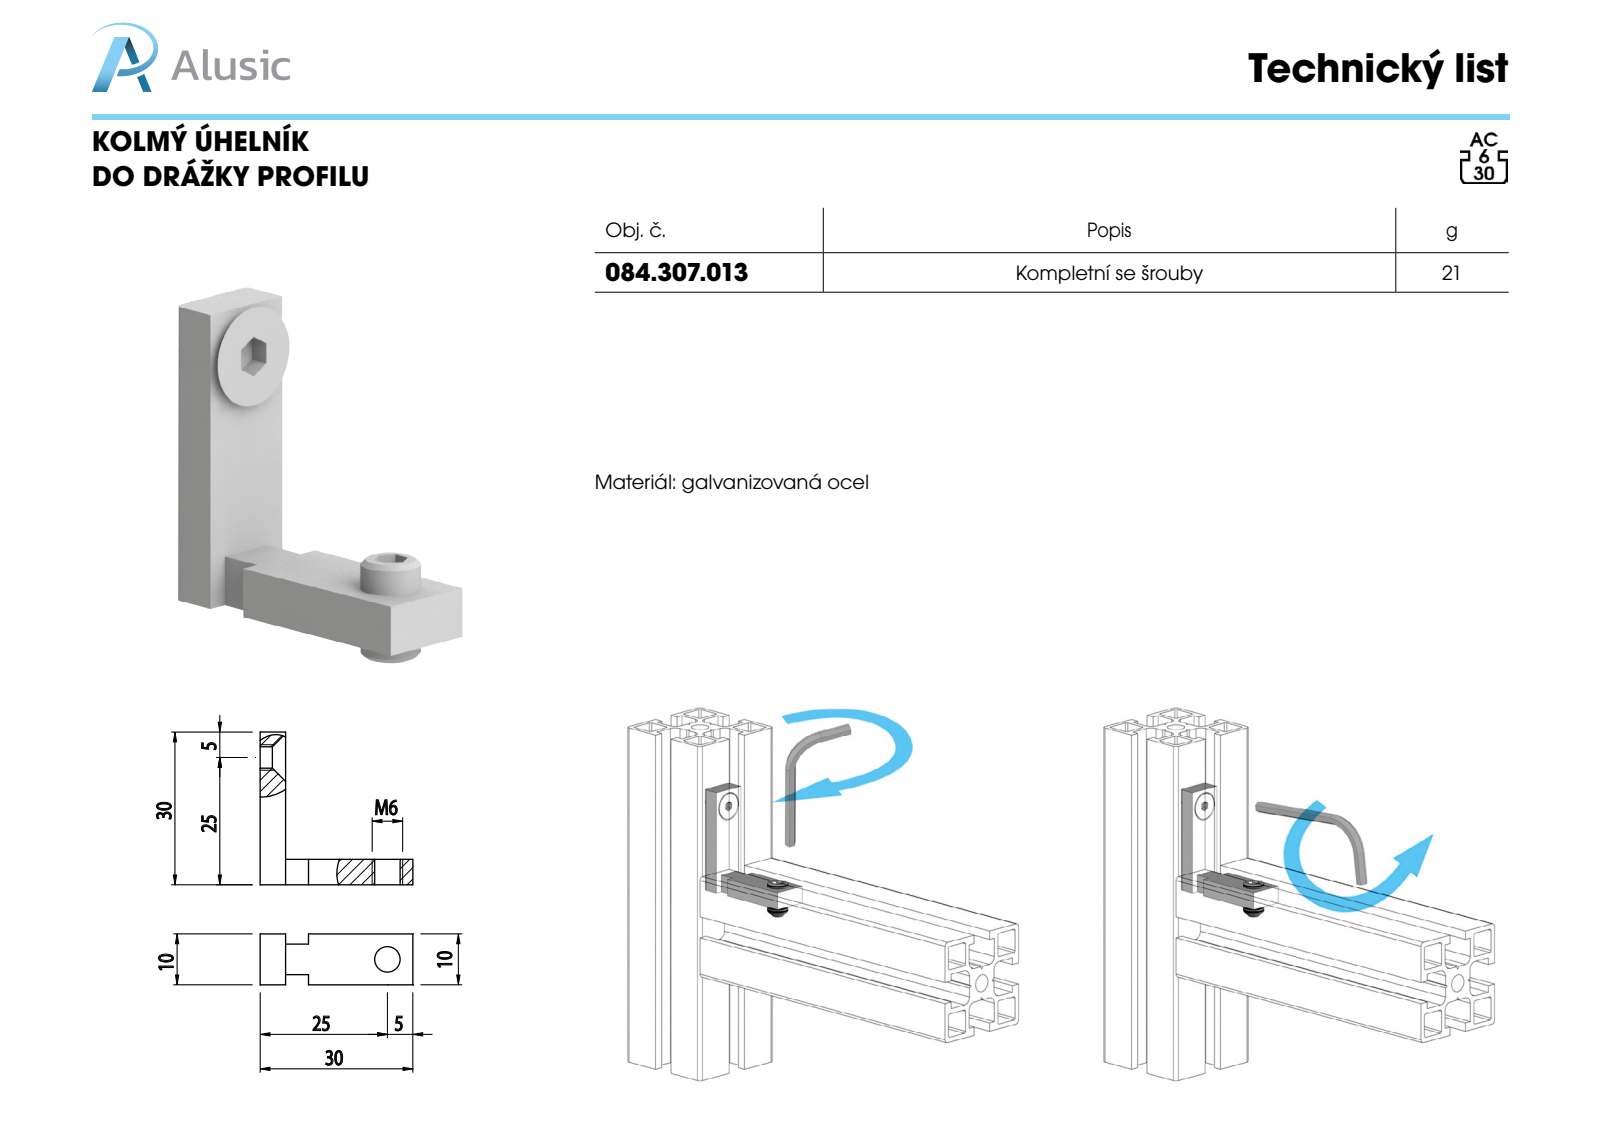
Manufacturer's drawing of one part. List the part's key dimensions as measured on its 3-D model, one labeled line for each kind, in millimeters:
Part name (STEP PRODUCT): 084.307.013
STEP written by: SolidWorks 2011 (CONFIG_CONTROL_DESIGN)
Units: millimetres
Bodies: 1 solid, 22 faces (14 planar, 6 cylindrical, 2 other)
Overall size (bounding box): 30 × 30 × 10
Volume: 2 450 mm³ · Surface area: 1 800 mm²
Round holes (diameter × count): ⌀4.2 ×1, ⌀5 ×1
Partial cylindrical surfaces — rounded edges, fillets, slot ends (radius × count): R0.8 ×2
Main face-to-face distances: 5, 10, 30, 25, 2, 8, 6, 9.5, 4.5, 20.5
